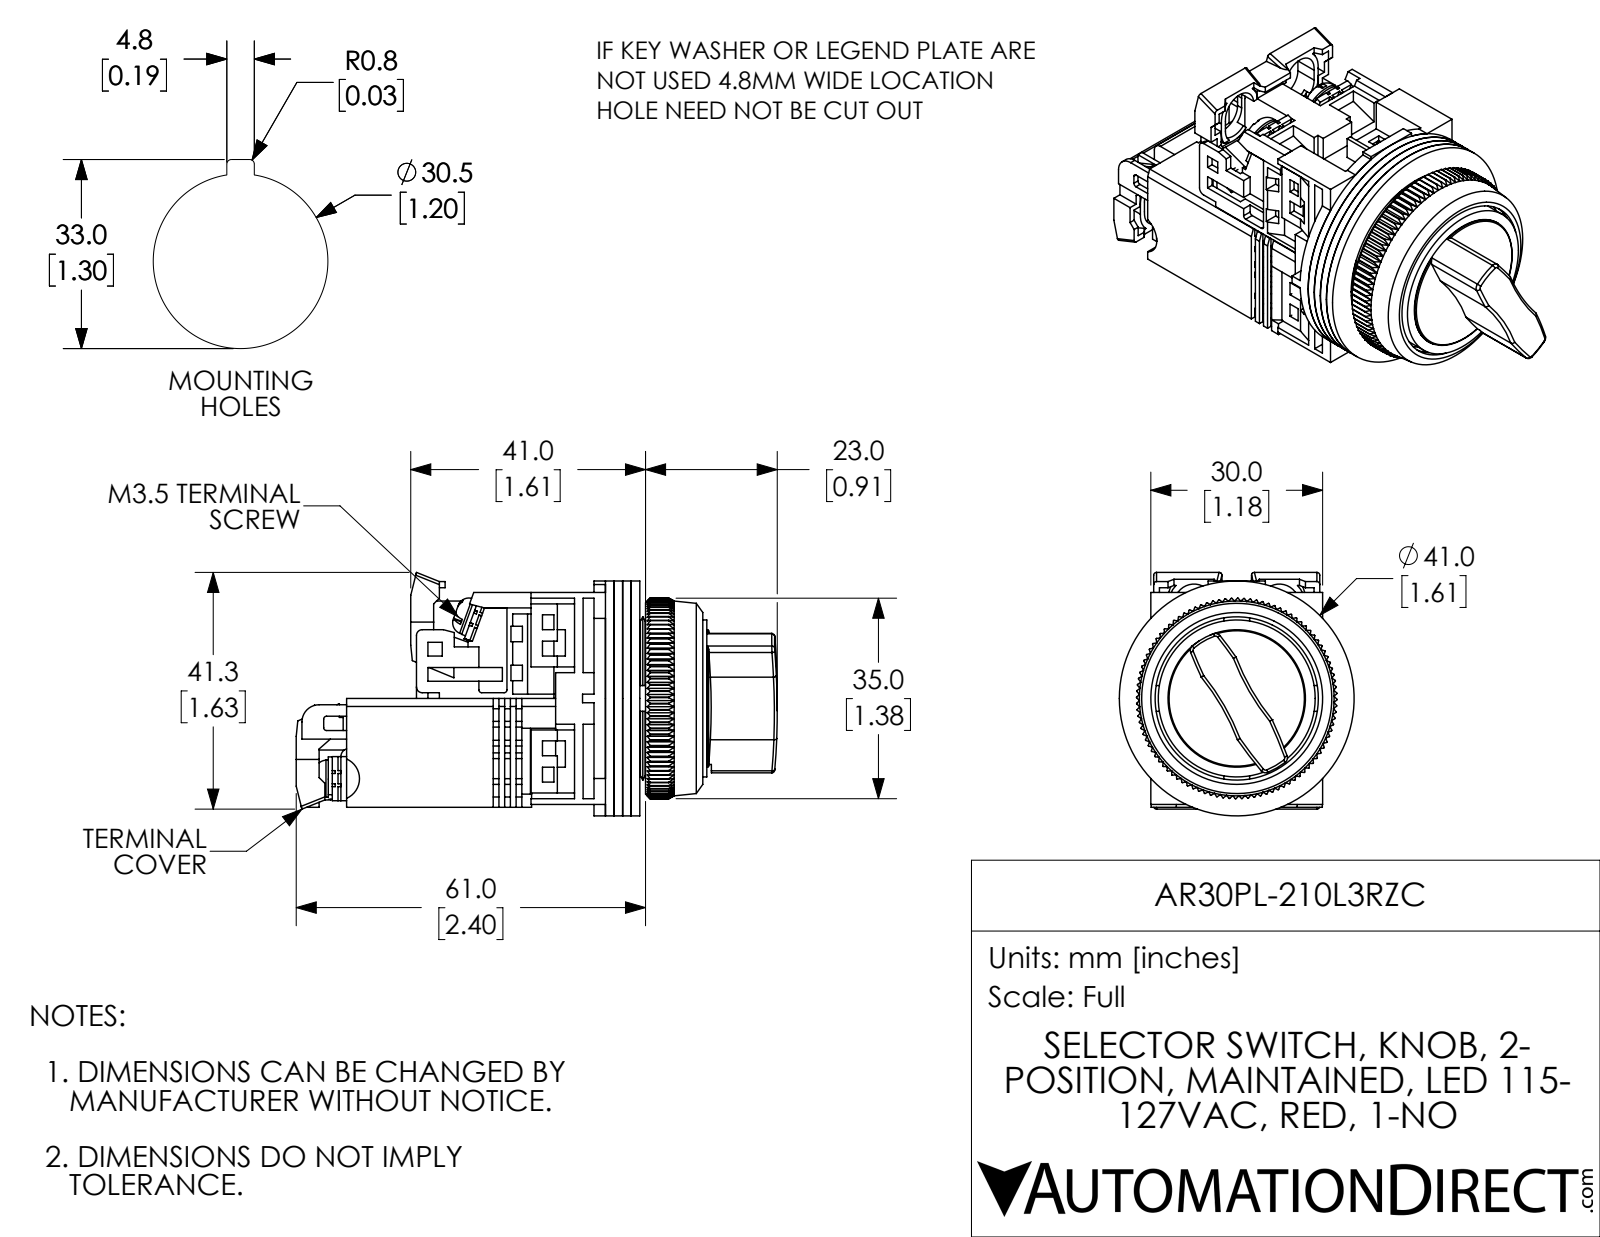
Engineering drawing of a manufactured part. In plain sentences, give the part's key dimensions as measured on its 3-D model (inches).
The part is named "AR30PL-210L3RZC". Its 3-D file was written by "SolidWorks 2017 (AUTOMOTIVE_DESIGN)". It is 27 solids with 2357 faces: 1706 planar, 321 cylindrical and 330 other. Overall it measures 3.307 by 1.673 by 1.614 inches. Its volume is 3.001 cubic inches and its surface area 63.38 square inches. Round holes: 6 of diameter 0.138, 4 of diameter 0.142, 3 of diameter 0.118, 1 of diameter 0.472, 1 of diameter 0.709, 1 of diameter 0.768, 1 of diameter 0.827, 1 of diameter 1.122, 1 of diameter 1.181, 1 of diameter 1.252. Round bosses or shafts: 4 of diameter 0.26, 2 of diameter 0.138, 2 of diameter 0.063, 1 of diameter 1.614, 1 of diameter 1.15, 1 of diameter 1.079, 1 of diameter 0.945, 1 of diameter 0.886. Partial cylindrical surfaces (rounded edges, fillets, slot ends): 17 of radius 0.059, 13 of radius 0.02, 6 of radius 0.039, 4 of radius 0.138, 4 of radius 0.177, 2 of radius 0.118, 2 of radius 1.575, 2 of radius 2.953. The main face-to-face distances are 0.059, 0.118, 0.177, 0.079, 0.039, 0.748, 0.787, 0.197, 0.256, 1.417. The hole center spacings are 0.579, 0.297, 0.624, 0.02, 0.302, 0.583, 0.583, 0.606.
